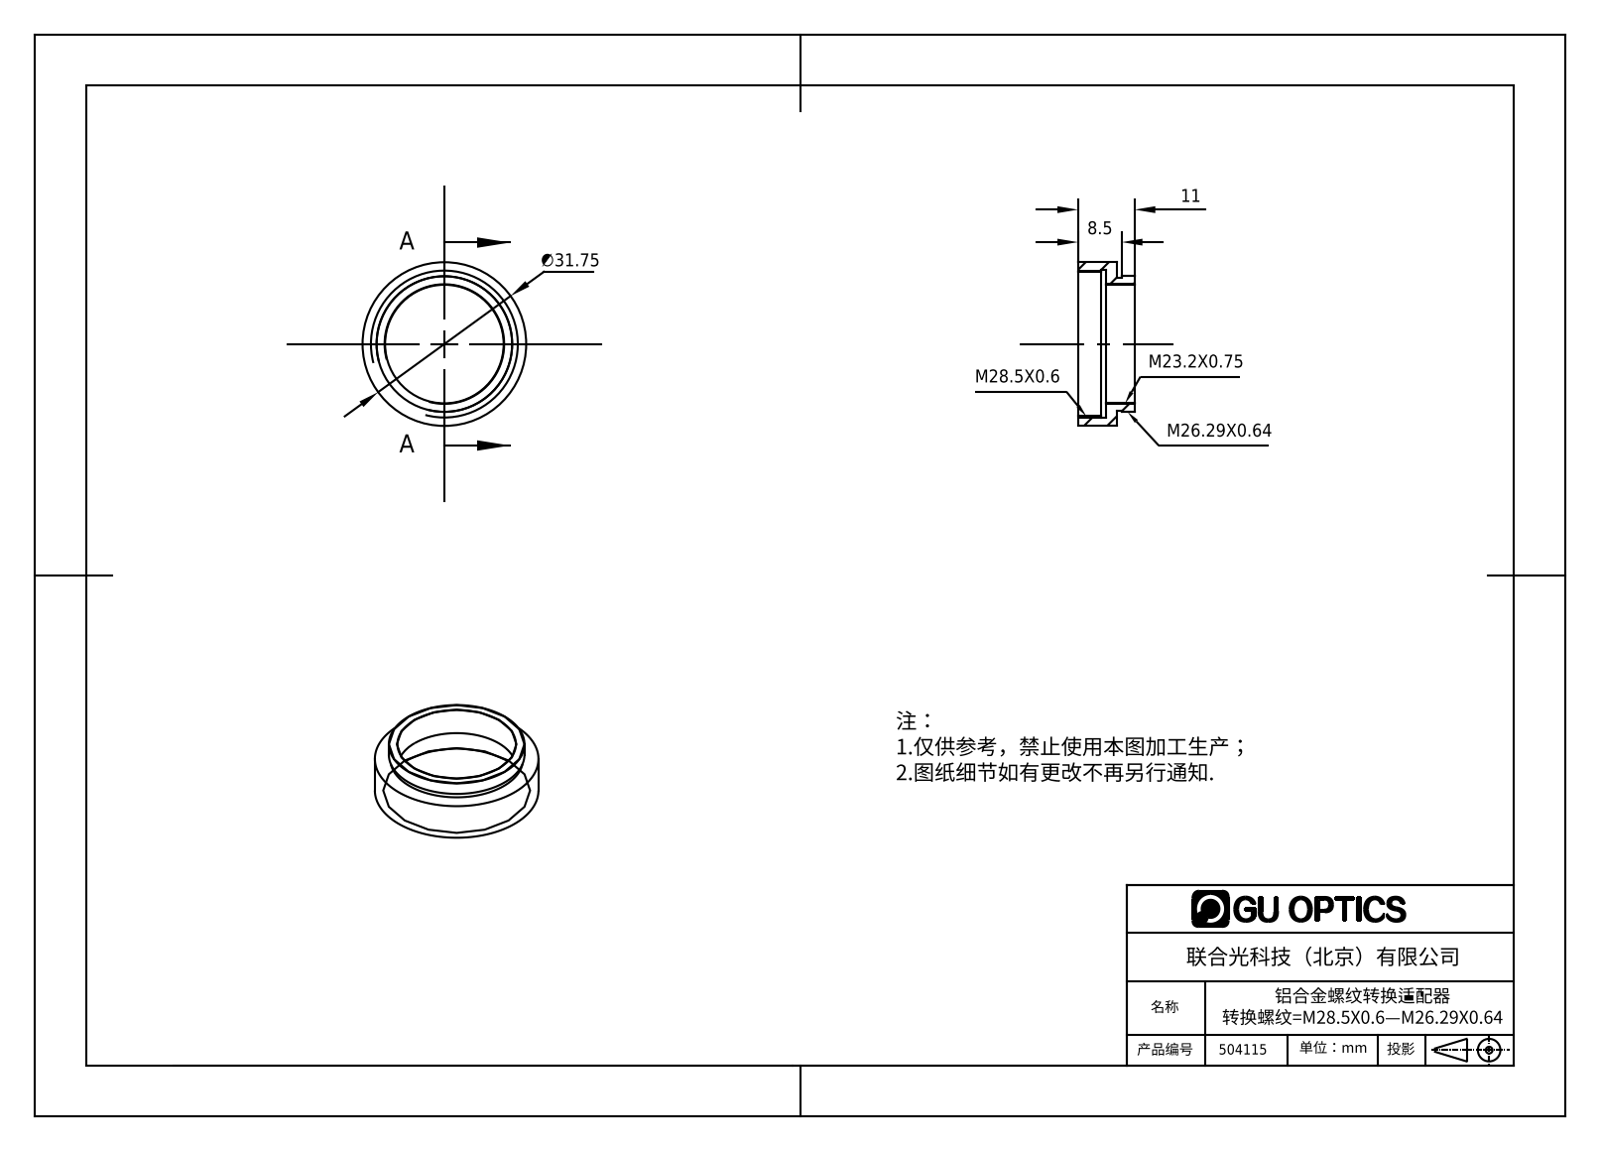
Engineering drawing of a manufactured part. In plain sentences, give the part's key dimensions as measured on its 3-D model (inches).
The part is named "504115". Its 3-D file was written by "SolidWorks 2016 (AUTOMOTIVE_DESIGN)". It is 1 solid with 18 faces: 6 planar, 12 cylindrical and 0 other. Overall it measures 1.25 by 1.25 by 0.433 inches. Its volume is 0.129 cubic inches and its surface area 4.304 square inches. Round holes: 1 of diameter 0.906, 1 of diameter 1.102, 1 of diameter 1.13. Round bosses or shafts: 1 of diameter 1.25, 1 of diameter 1.036, 1 of diameter 1.016. The main face-to-face distances are 0.217, 0.079, 0.295, 0.433, 0.138, 0.039, 0.118, 0.177, 0.256, 0.335.
